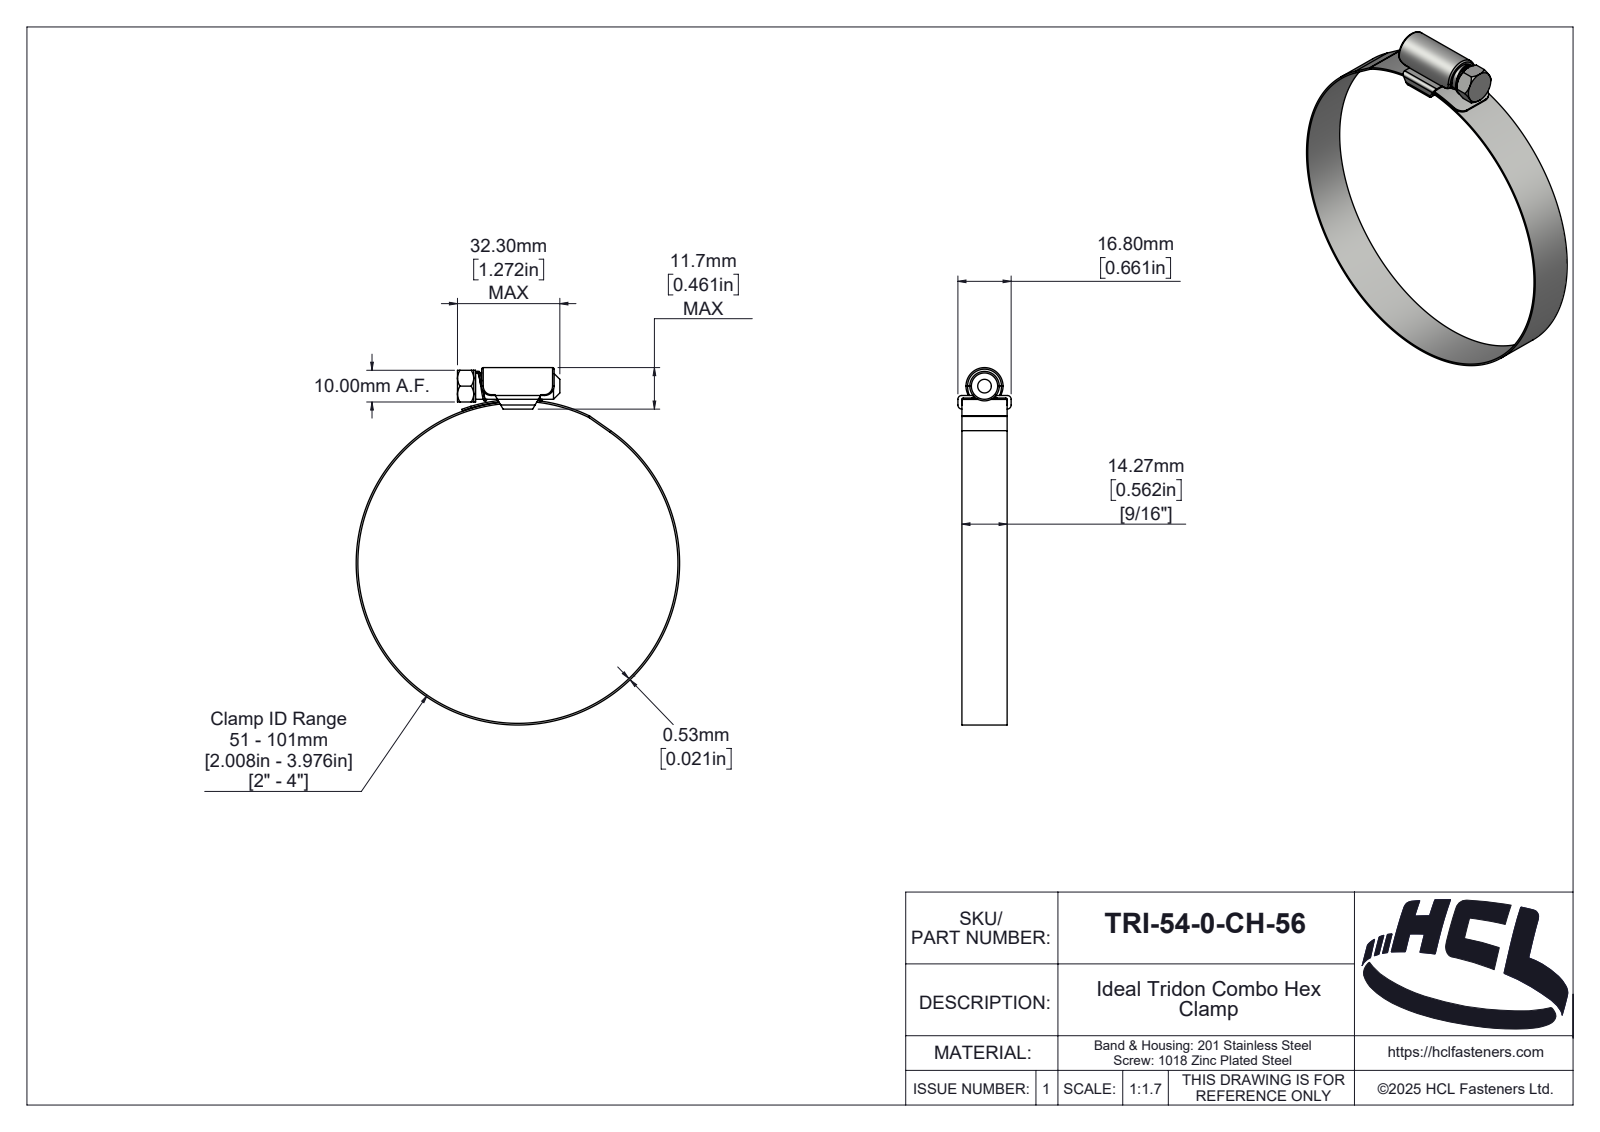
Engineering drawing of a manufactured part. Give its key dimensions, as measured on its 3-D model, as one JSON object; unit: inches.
{"part_name": "TRI-54-0-CH-56", "step_written_by": "SolidWorks 2025 (AUTOMOTIVE_DESIGN)", "units": "inches", "bodies": {"solids": 3, "faces": 212, "planar": 35, "cylindrical": 101, "other": 76}, "overall_size": [4.438, 4.018, 0.661], "volume_in3": 0.332, "surface_area_in2": 20.1, "round_holes": [[3.976, 1]], "round_bosses_or_shafts": [[4.018, 1], [0.394, 1], [0.327, 1]], "partial_cylinders_radius": [[0.02, 6], [0.118, 4], [0.004, 2], [0.047, 2], [0.051, 2], [0.018, 1], [0.074, 1], [0.079, 1]], "face_to_face_distances": [0.561, 0.047, 0.021, 0.138, 0.091, 0.169, 0.122, 0.031, 0.393, 0.05]}
